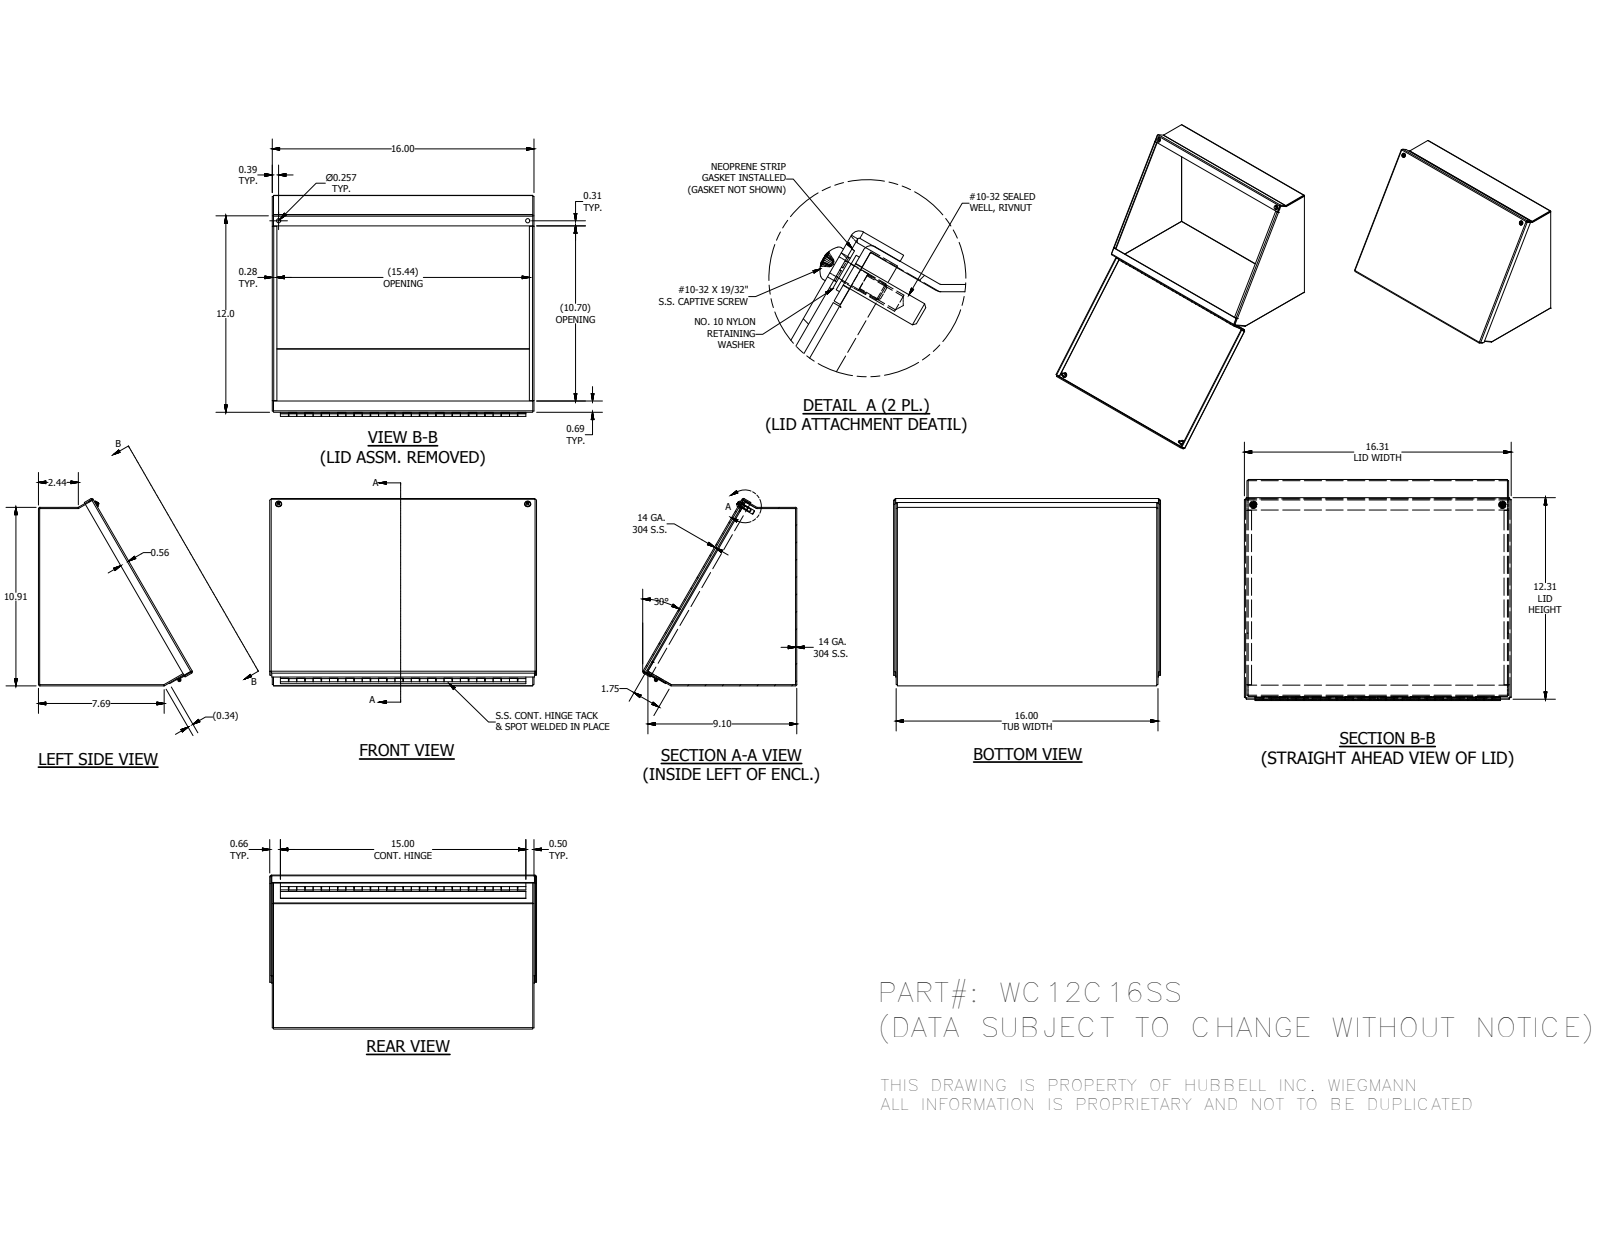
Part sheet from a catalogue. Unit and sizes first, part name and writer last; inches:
Units: inches
Overall size (bounding box): 16.313 × 11.452 × 9.413
Round holes (diameter × count): ⌀0.156 ×2, ⌀0.196 ×2, ⌀0.257 ×2, ⌀0.278 ×2, ⌀0.281 ×2, ⌀0.117 ×1
Round bosses / shafts (diameter × count): ⌀0.453 ×2, ⌀0.406 ×2, ⌀0.373 ×2, ⌀0.248 ×2, ⌀0.19 ×2, ⌀0.2 ×1, ⌀0.1 ×1
Partial cylindrical surfaces — rounded edges, fillets, slot ends (radius × count): R0.016 ×12, R0.09 ×12, R0.089 ×2
Main face-to-face distances: 0.074, 15.926, 10.832, 15.852, 16, 10.758, 10.906, 0.168, 12, 0.156
Hole centre spacings: 15.226
Volume: 57.53 in³ · Surface area: 1 600 in²
Bodies: 13 solids, 447 faces (282 planar, 113 cylindrical, 52 other)
Part name (STEP PRODUCT): WC12C16SSBTB; WC12C16SSLID; WC12CSSLS; WC12CSSRS (+8 more)
STEP written by: Autodesk Inventor 2014 (AUTOMOTIVE_DESIGN)
